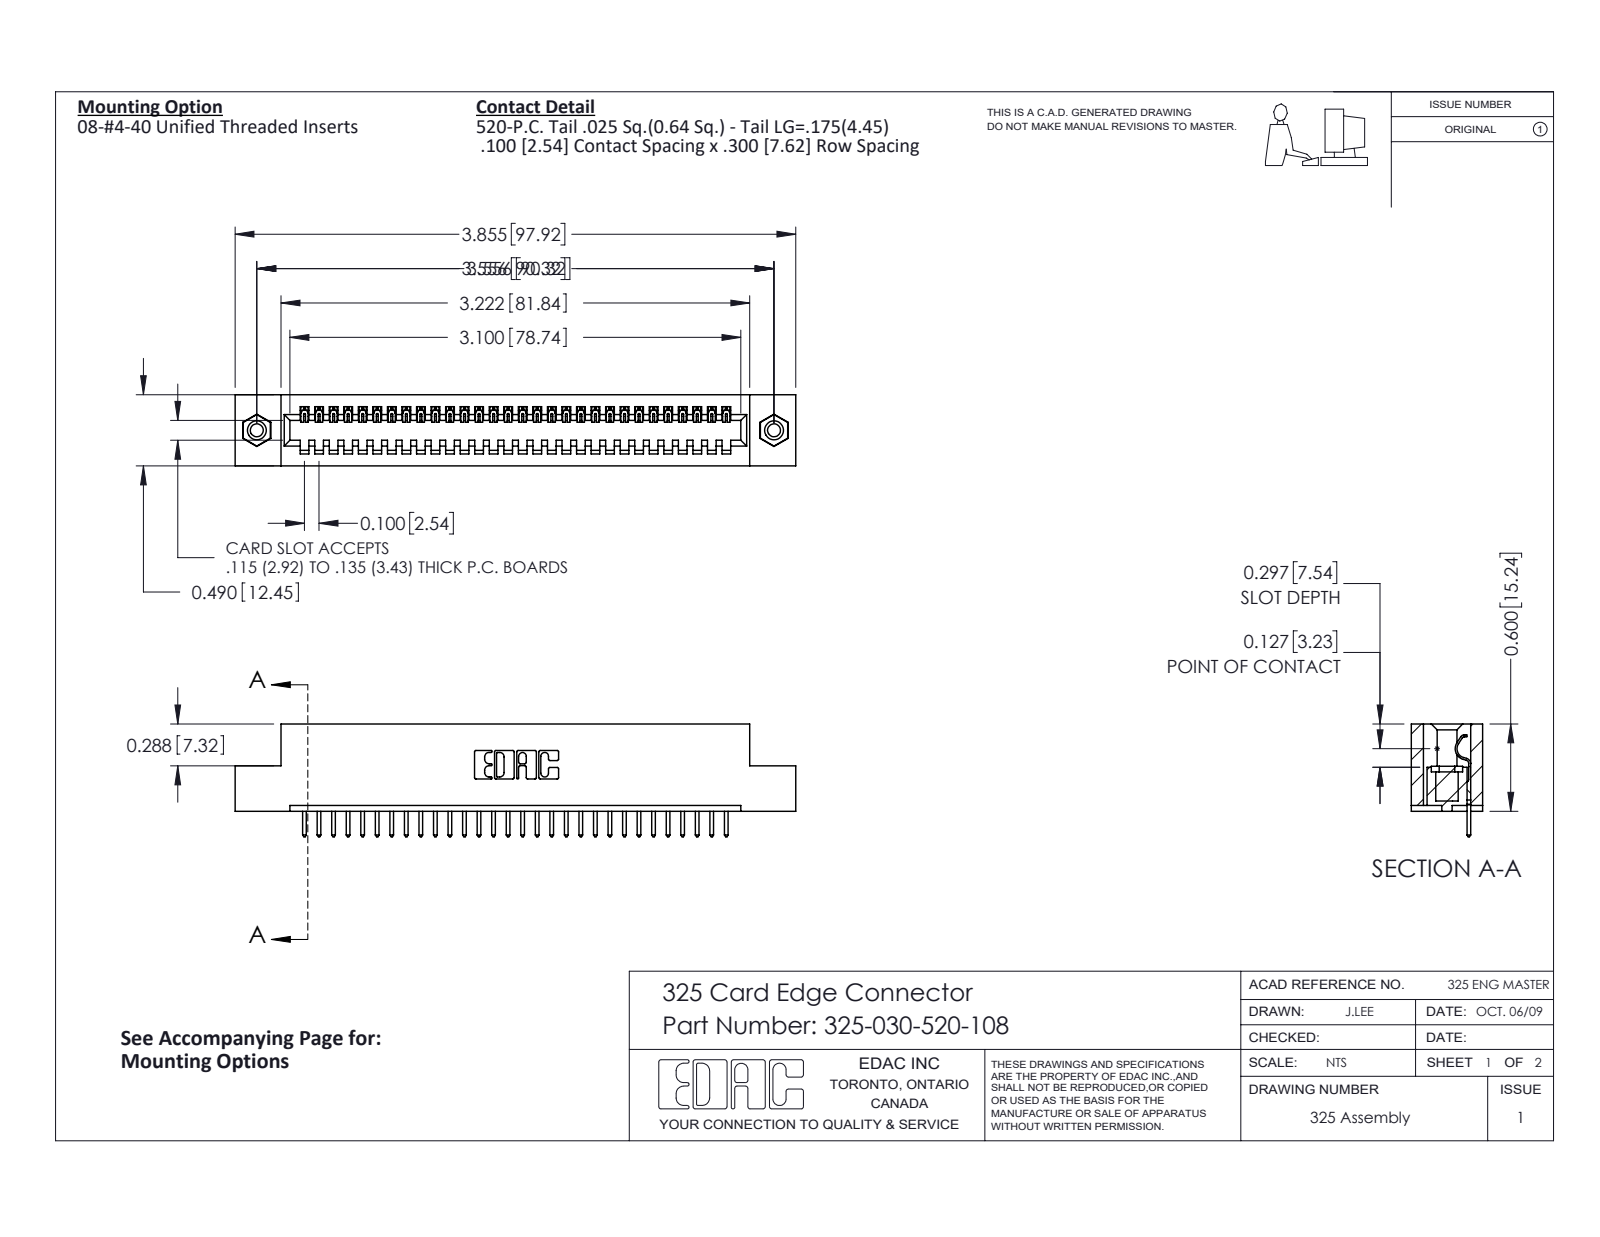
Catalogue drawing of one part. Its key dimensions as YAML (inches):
part_name: "345-250-001_345-250-003-102; 325 Part_TI; 325-030-520-108; 325-292-001_325-293-120"
step_written_by: "SolidWorks 2016 (CONFIG_CONTROL_DESIGN)"
units: inches
bodies: {solids: 33, faces: 1914, planar: 1362, cylindrical: 536, other: 16}
overall_size: [3.855, 0.775, 0.49]
volume: 0.748
surface_area: 19.97
round_holes:
  - {diameter: 0.089, count: 2}
  - {diameter: 0.125, count: 2}
  - {diameter: 0.16, count: 2}
round_bosses_or_shafts:
  - {diameter: 0.155, count: 2}
partial_cylinders:
  - {radius: 0.006, count: 60}
  - {radius: 0.01, count: 60}
  - {radius: 0.01, count: 22}
  - {radius: 0.007, count: 6}
  - {radius: 0.031, count: 6}
  - {radius: 0.026, count: 3}
  - {radius: 0.014, count: 1}
  - {radius: 0.022, count: 1}
face_to_face_distances: [0.083, 0.407, 0.49, 0.3, 0.107, 0.383, 0.025, 0.325, 0.04, 0.56]
hole_center_spacings: [3.556]
